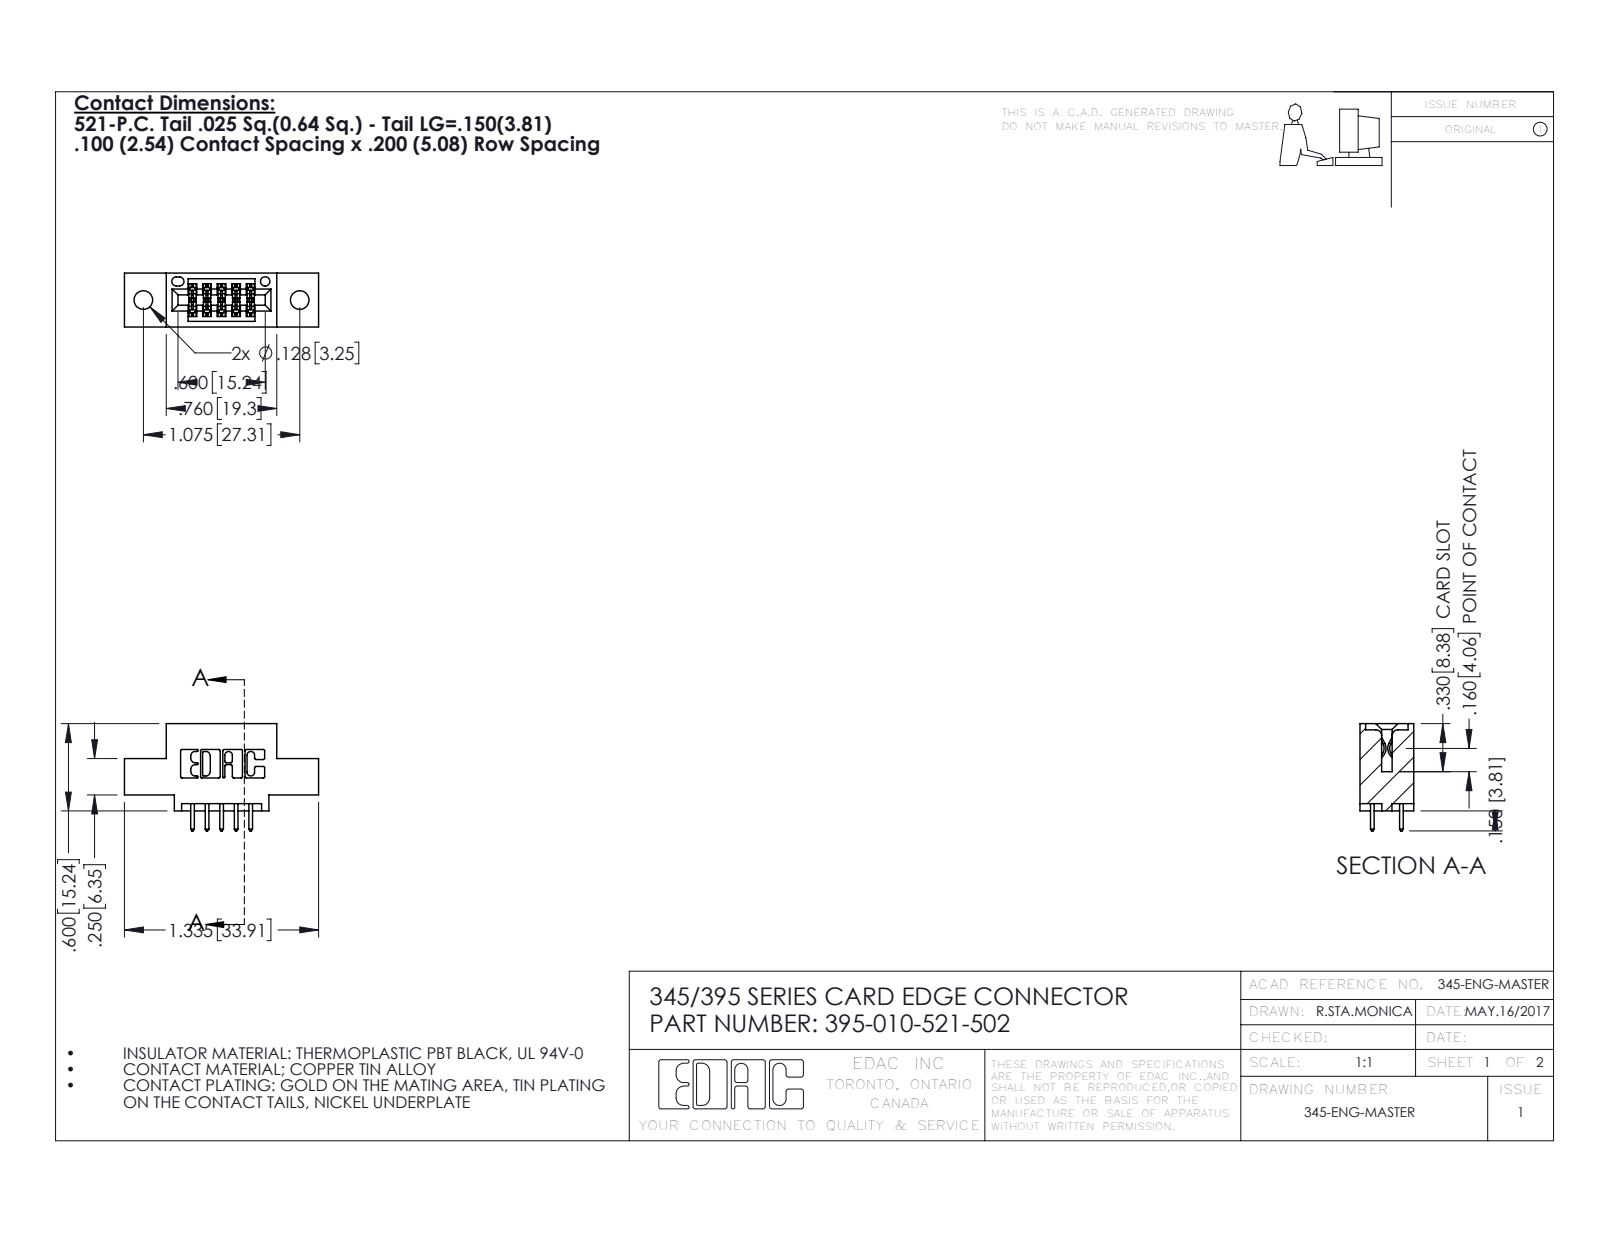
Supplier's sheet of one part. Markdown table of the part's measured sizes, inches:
| quantity | value |
| --- | --- |
| part name | 395-010-521-502; 345 Part_0.110 Offset - 0.128 Dia; 345-292-001_345-293-121 |
| STEP written by | SolidWorks 2016 (CONFIG_CONTROL_DESIGN) |
| units | inches |
| bodies | 11 solids, 630 faces (414 planar, 216 cylindrical, 0 other) |
| overall size | 1.335 × 0.737 × 0.37 |
| volume | 0.173 in³ |
| surface area | 5.068 in² |
| round holes (diameter × count) | 0.128 × 2, 0.064 × 1 |
| partial cylindrical surfaces (radius × count) | 0.01 × 22, 0.006 × 15, 0.01 × 10, 0.007 × 6, 0.031 × 6, 0.026 × 3, 0.014 × 2, 0.019 × 2 |
| main face-to-face distances | 0.2, 0.37, 0.298, 0.072, 0.1, 0.025, 0.25, 0.098, 0.272, 0.225 |
| hole center spacings | 0.27, 0.847, 1.075 |
